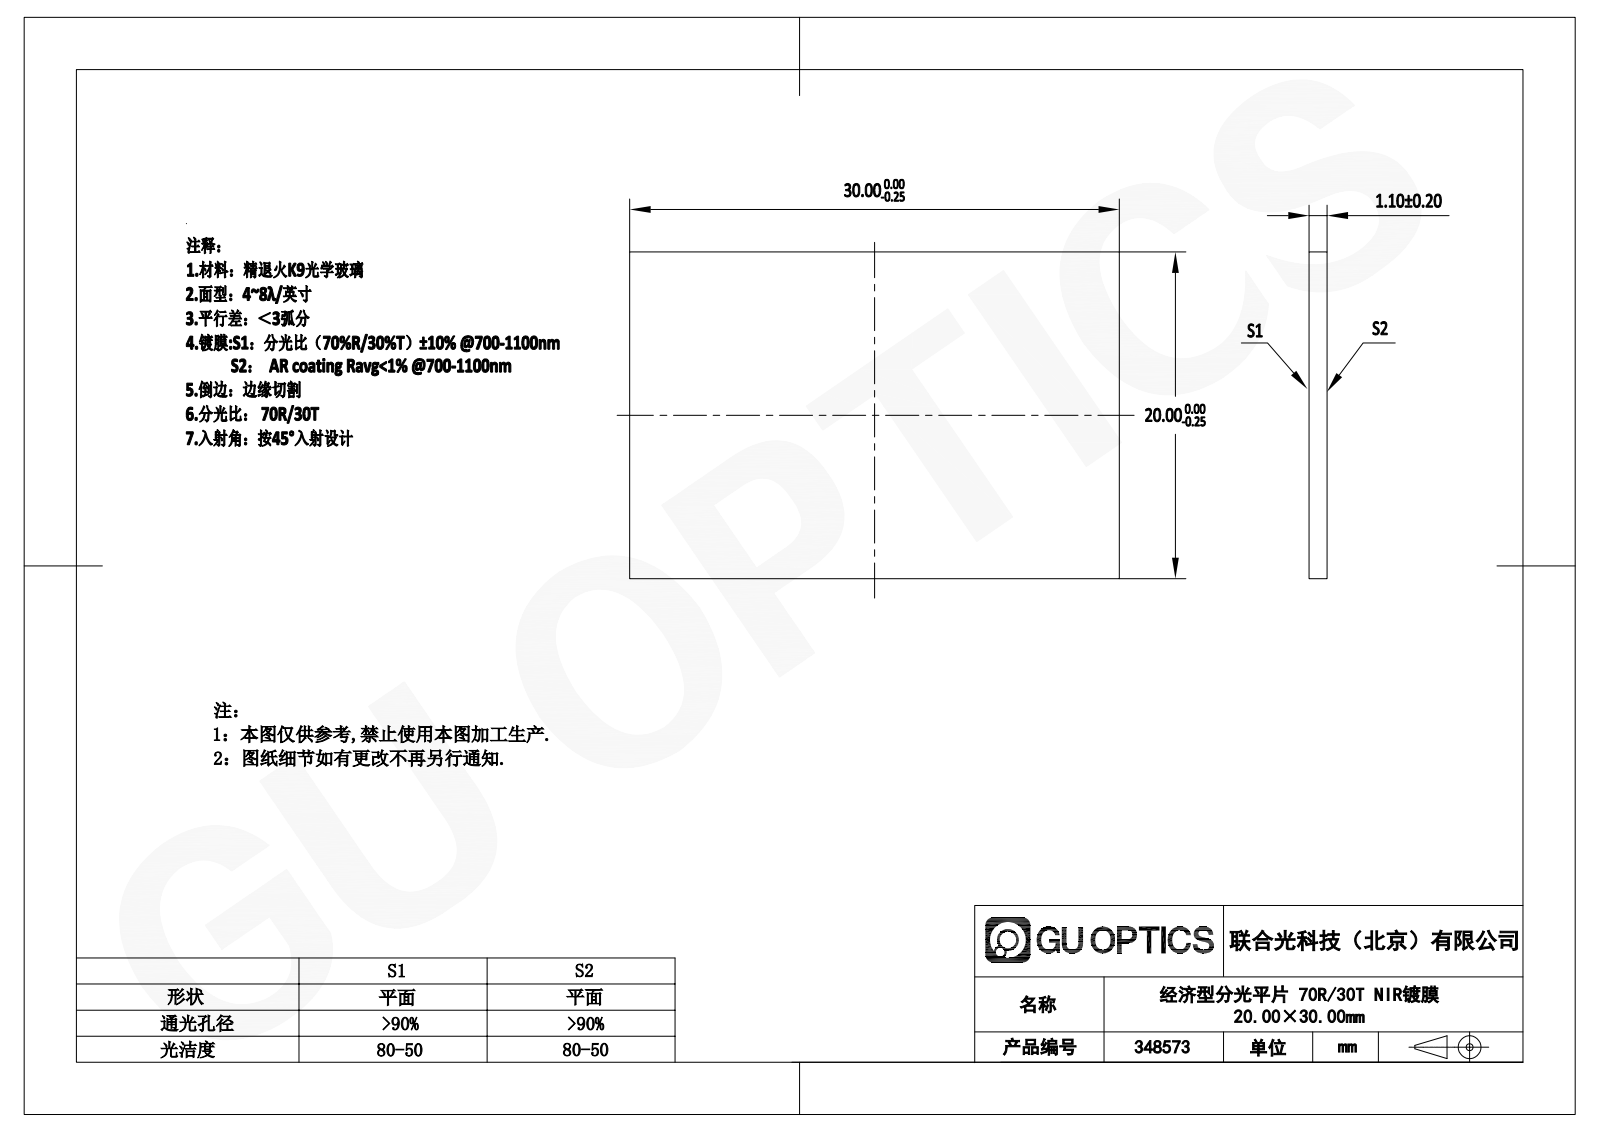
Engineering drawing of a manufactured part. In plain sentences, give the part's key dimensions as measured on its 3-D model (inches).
The part is named "348503". Its 3-D file was written by "SolidWorks 2016 (CONFIG_CONTROL_DESIGN)". It is 1 solid with 6 faces: 6 planar, 0 cylindrical and 0 other. Overall it measures 1.181 by 0.787 by 0.043 inches. Its volume is 0.04 cubic inches and its surface area 2.031 square inches. The main face-to-face distances are 0.043, 0.787, 1.181.
